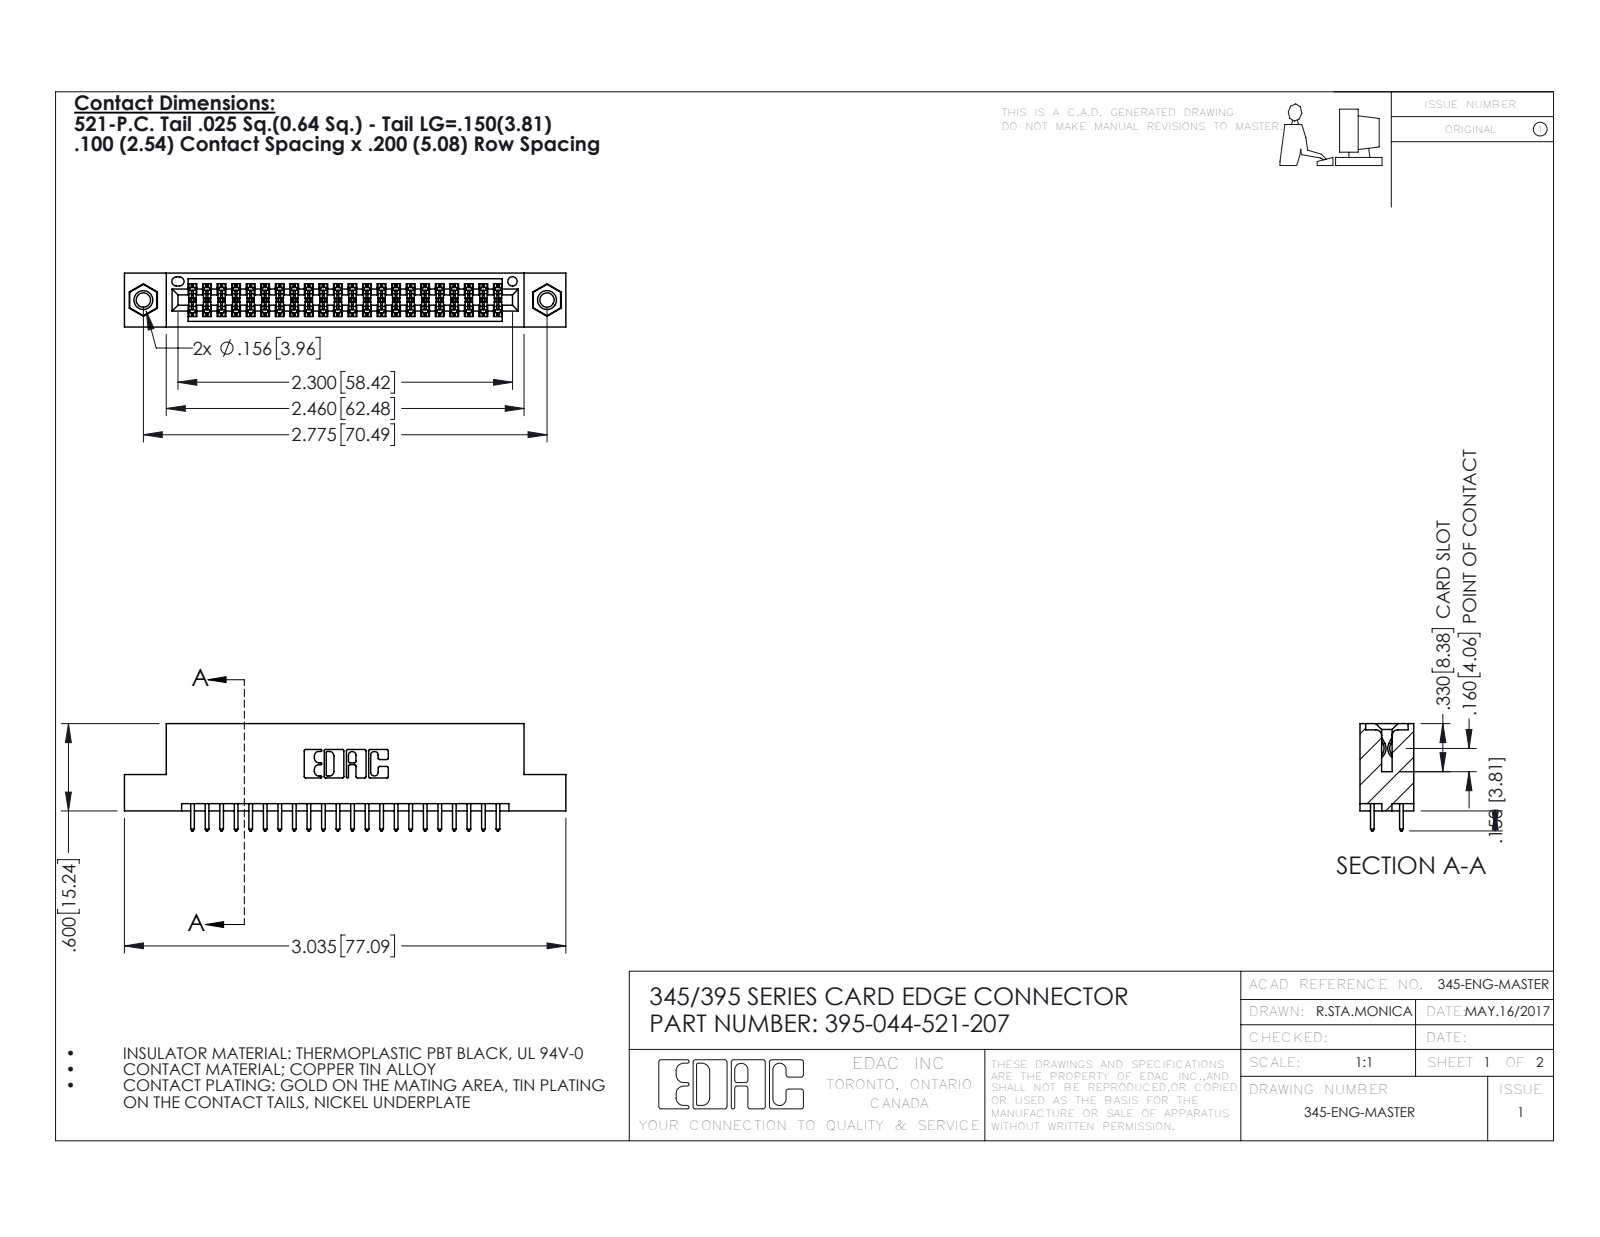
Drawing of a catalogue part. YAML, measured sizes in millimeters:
part_name: "345-292-001_345-293-121; 345-250-001_345-250-005-103; 345 Part_Flush Mounting Lugs - 0.156 Dia-TI; 395-044-521-207"
step_written_by: "SolidWorks 2016 (CONFIG_CONTROL_DESIGN)"
units: millimeters
bodies: {solids: 47, faces: 2386, planar: 1564, cylindrical: 806, other: 16}
overall_size: [77.1, 18.7, 9.4]
volume: 7280
surface_area: 10270
round_holes:
  - {diameter: 2.5, count: 2}
  - {diameter: 3.2, count: 2}
  - {diameter: 4, count: 2}
  - {diameter: 1.6, count: 1}
round_bosses_or_shafts:
  - {diameter: 3.9, count: 2}
partial_cylinders:
  - {radius: 0.2, count: 66}
  - {radius: 0.3, count: 44}
  - {radius: 0.3, count: 22}
  - {radius: 0.2, count: 6}
  - {radius: 0.8, count: 6}
  - {radius: 0.7, count: 3}
  - {radius: 0.4, count: 2}
  - {radius: 0.5, count: 2}
face_to_face_distances: [1.8, 7.6, 5.1, 9.4, 2.5, 6.9, 0.6, 5.7, 4.4, 3.8]
hole_center_spacings: [6.9, 64.5, 70.5]
